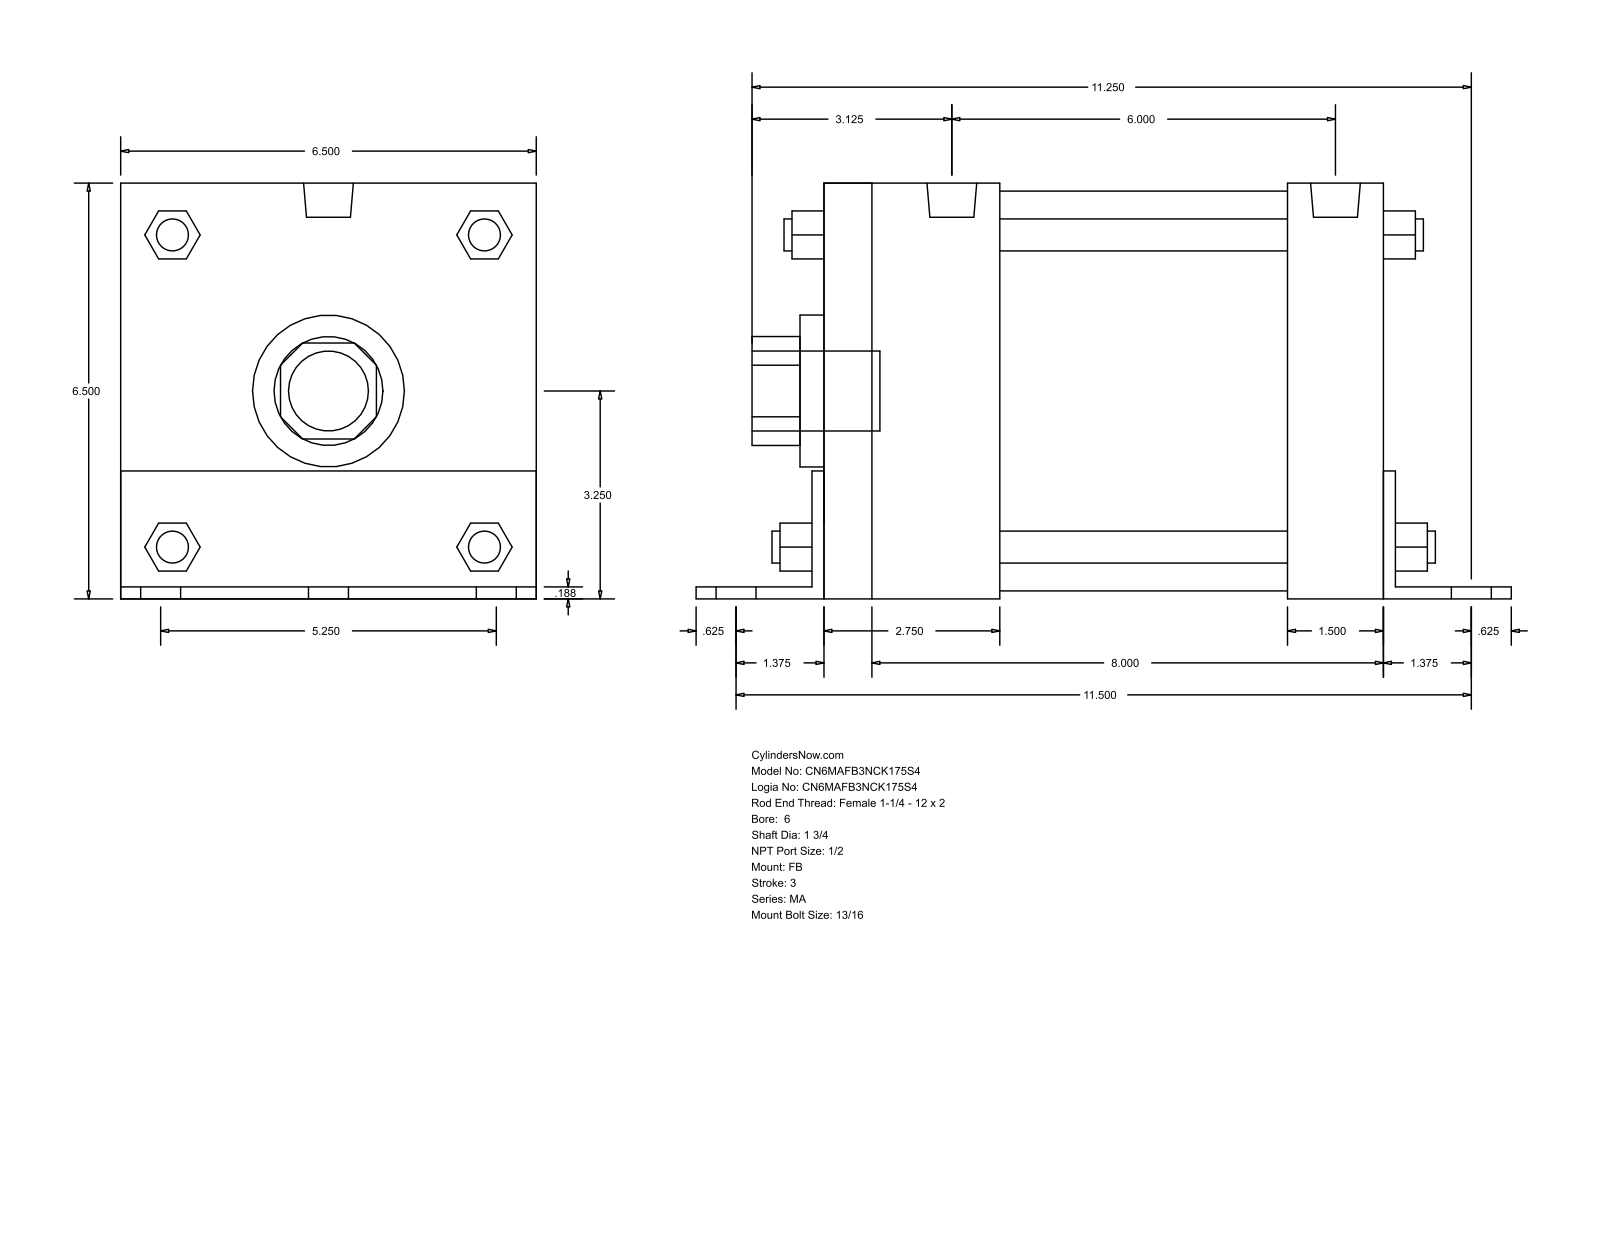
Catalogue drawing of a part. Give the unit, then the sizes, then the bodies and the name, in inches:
Units: inches
Overall size (bounding box): 12.75 × 6.502 × 6.5
Round holes (diameter × count): ⌀1.75 ×1, ⌀2.375 ×1, ⌀6.25 ×1
Round bosses / shafts (diameter × count): ⌀0.813 ×6, ⌀0.687 ×4, ⌀0.5 ×4, ⌀0.778 ×2, ⌀1.25 ×1
Partial cylindrical surfaces — rounded edges, fillets, slot ends (radius × count): R0.852 ×1, R1.262 ×1
Main face-to-face distances: 6.5, 0.187, 8.75, 6.502, 0.185, 6.315, 1.5, 0.188, 8.938, 8.937
Bodies: 0 solids, 140 faces (105 planar, 35 cylindrical, 0 other)
Part name (STEP PRODUCT): MA_FB__0600_1.75
STEP written by: GSSL Pune (CONFIG_CONTROL_DESIGN)
